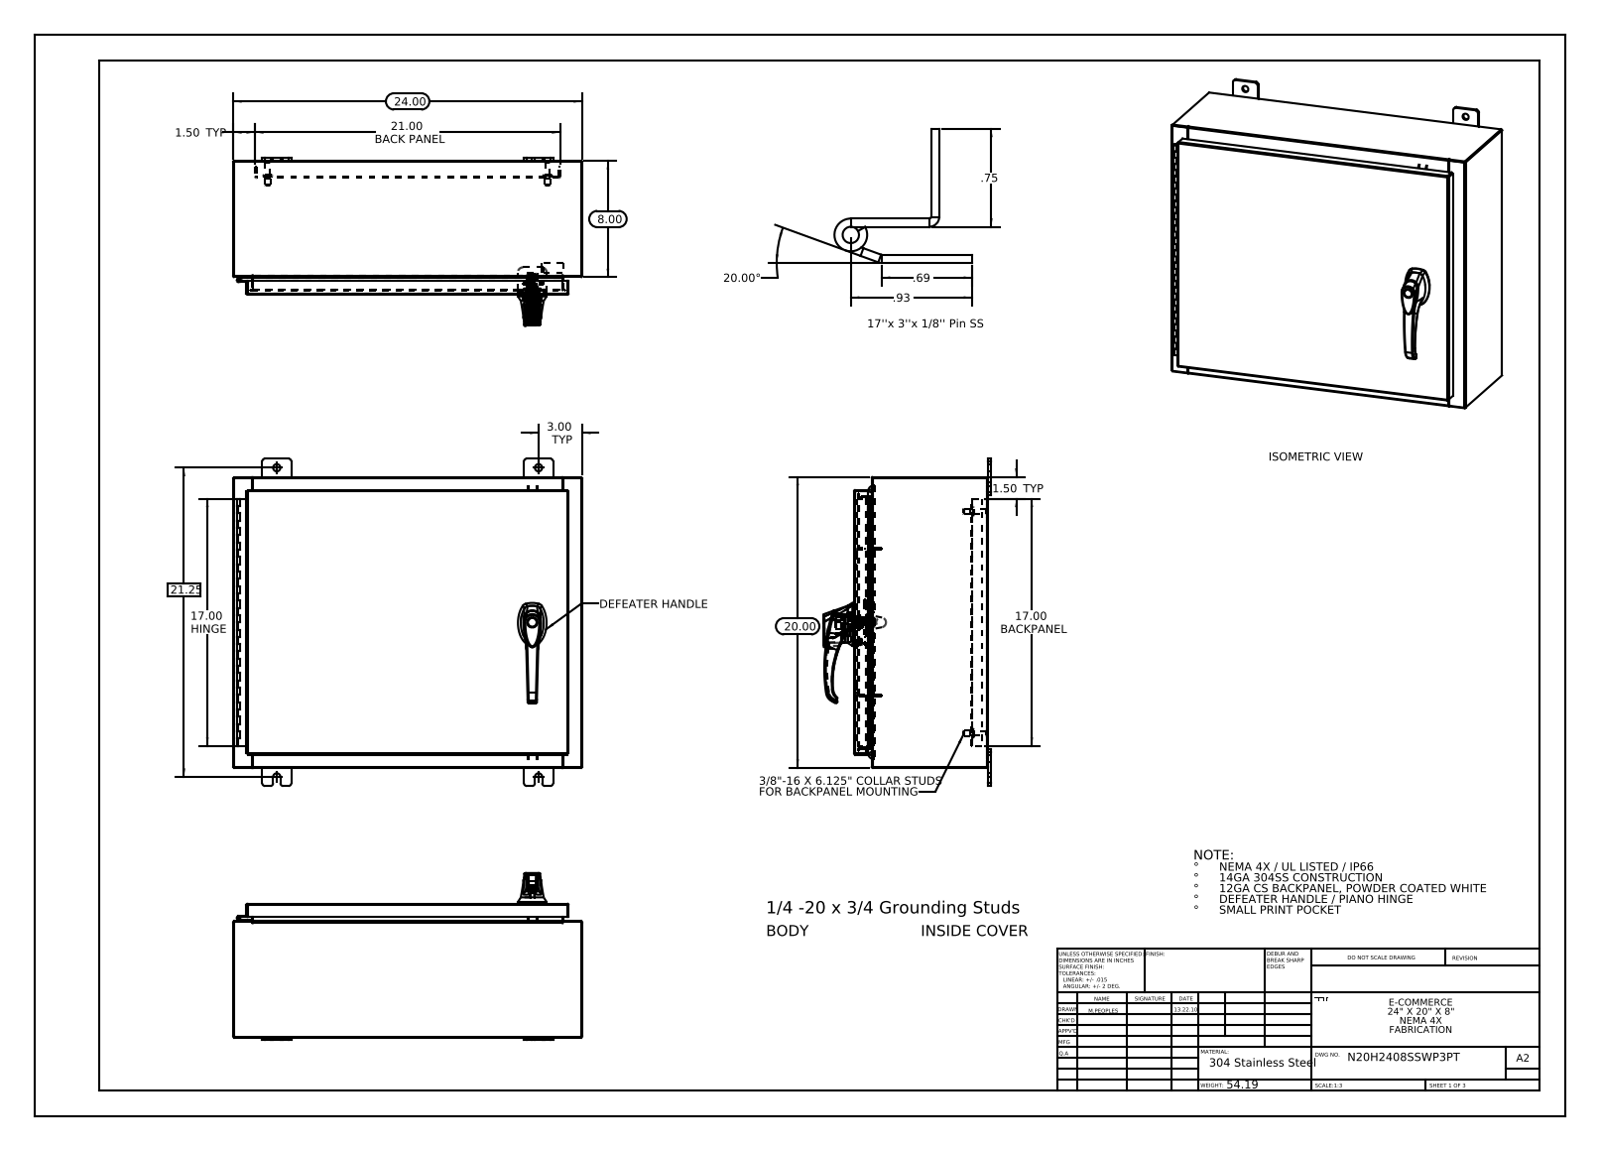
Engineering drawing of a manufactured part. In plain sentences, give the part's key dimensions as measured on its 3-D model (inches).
The part is named "26161102; N20H2408SSWP3PT; 297025; N20H2408SSWP3PT 263033_Industrilas (+8 more)". Its 3-D file was written by "SolidWorks 2013 (CONFIG_CONTROL_DESIGN)". It is 31 solids with 2316 faces: 817 planar, 845 cylindrical and 654 other. Overall it measures 24 by 22.5 by 11.495 inches. Its volume is 192.6 cubic inches and its surface area 4 759 square inches. Round holes: 8 of diameter 0.5, 4 of diameter 0.25, 3 of diameter 0.138, 3 of diameter 0.161, 2 of diameter 0.079, 2 of diameter 0.203, 2 of diameter 0.313, 2 of diameter 0.437, 1 of diameter 0.125, 1 of diameter 0.125, 1 of diameter 0.197, 1 of diameter 0.276. Round bosses or shafts: 4 of diameter 0.625, 4 of diameter 0.375, 4 of diameter 0.33, 1 of diameter 1.181, 1 of diameter 0.748, 1 of diameter 0.68, 1 of diameter 0.661, 1 of diameter 0.639. Partial cylindrical surfaces (rounded edges, fillets, slot ends): 37 of radius 0.118, 33 of radius 0.006, 24 of radius 0.19, 22 of radius 0.013, 18 of radius 0.088, 15 of radius 0.039, 12 of radius 0.028, 6 of radius 0.008. The main face-to-face distances are 0.075, 9.126, 9.051, 9.201, 0.104, 19.925, 1, 1.075, 8.051, 8.126. The hole center spacings are 3.404, 0.295, 0.625, 0.841, 1.25, 1.313, 1.561, 1.858.
